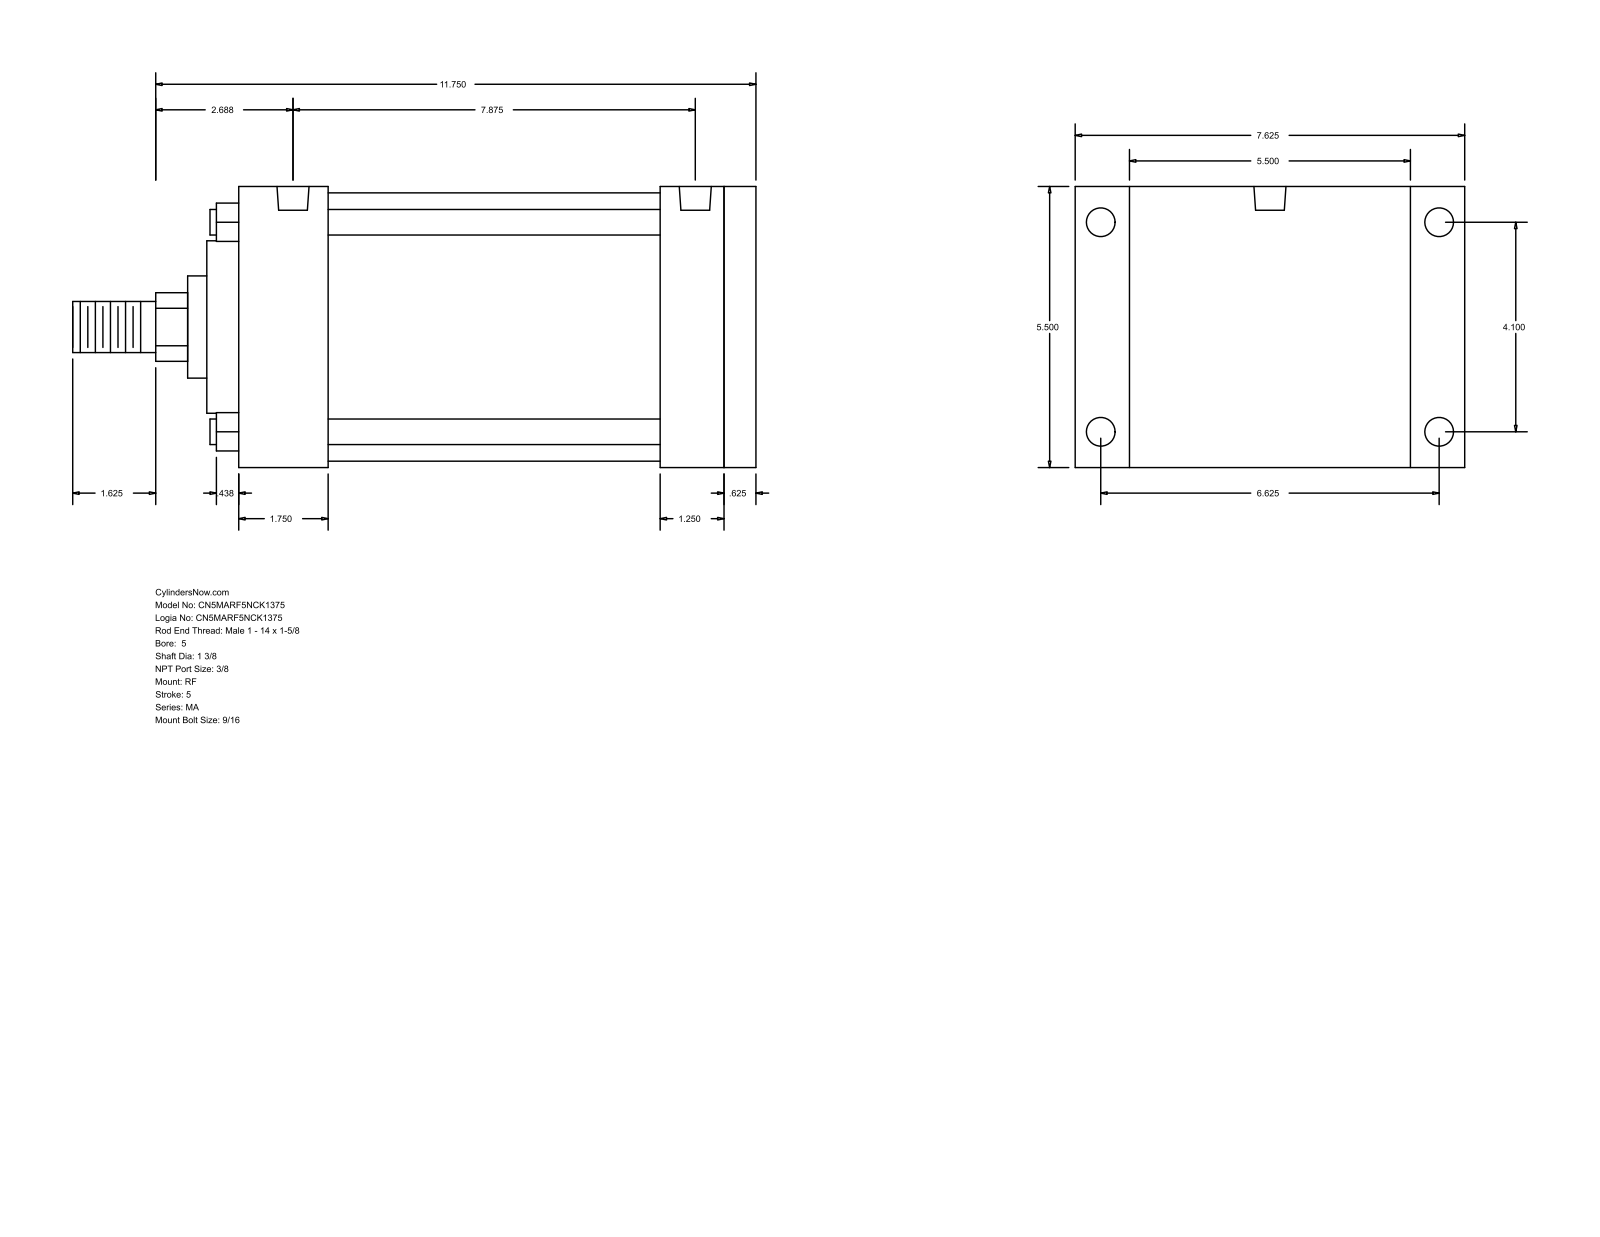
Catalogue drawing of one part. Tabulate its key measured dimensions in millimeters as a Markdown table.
| quantity | value |
| --- | --- |
| part name | MA_RF__0500_1.375 |
| STEP written by | GSSL Pune (CONFIG_CONTROL_DESIGN) |
| units | millimeters |
| bodies | 0 solids, 94 faces (65 planar, 29 cylindrical, 0 other) |
| overall size | 339.73 × 193.68 × 139.7 |
| round holes (diameter × count) | 11.11 × 4, 14.29 × 4, 15.93 × 2 |
| round bosses / shafts (diameter × count) | 12.7 × 4, 133.35 × 1, 85.72 × 1, 50.8 × 1, 34.92 × 1, 25.4 × 1 |
| partial cylindrical surfaces (radius × count) | 17.06 × 1 |
| main face-to-face distances | 139.7, 257.18, 15.88, 241.3, 44.45, 196.85, 212.73, 209.55, 165.1, 31.75 |
| hole center spacings | 4.77, 104.14, 168.28, 190.49, 195.26, 197.9, 200.03 |
